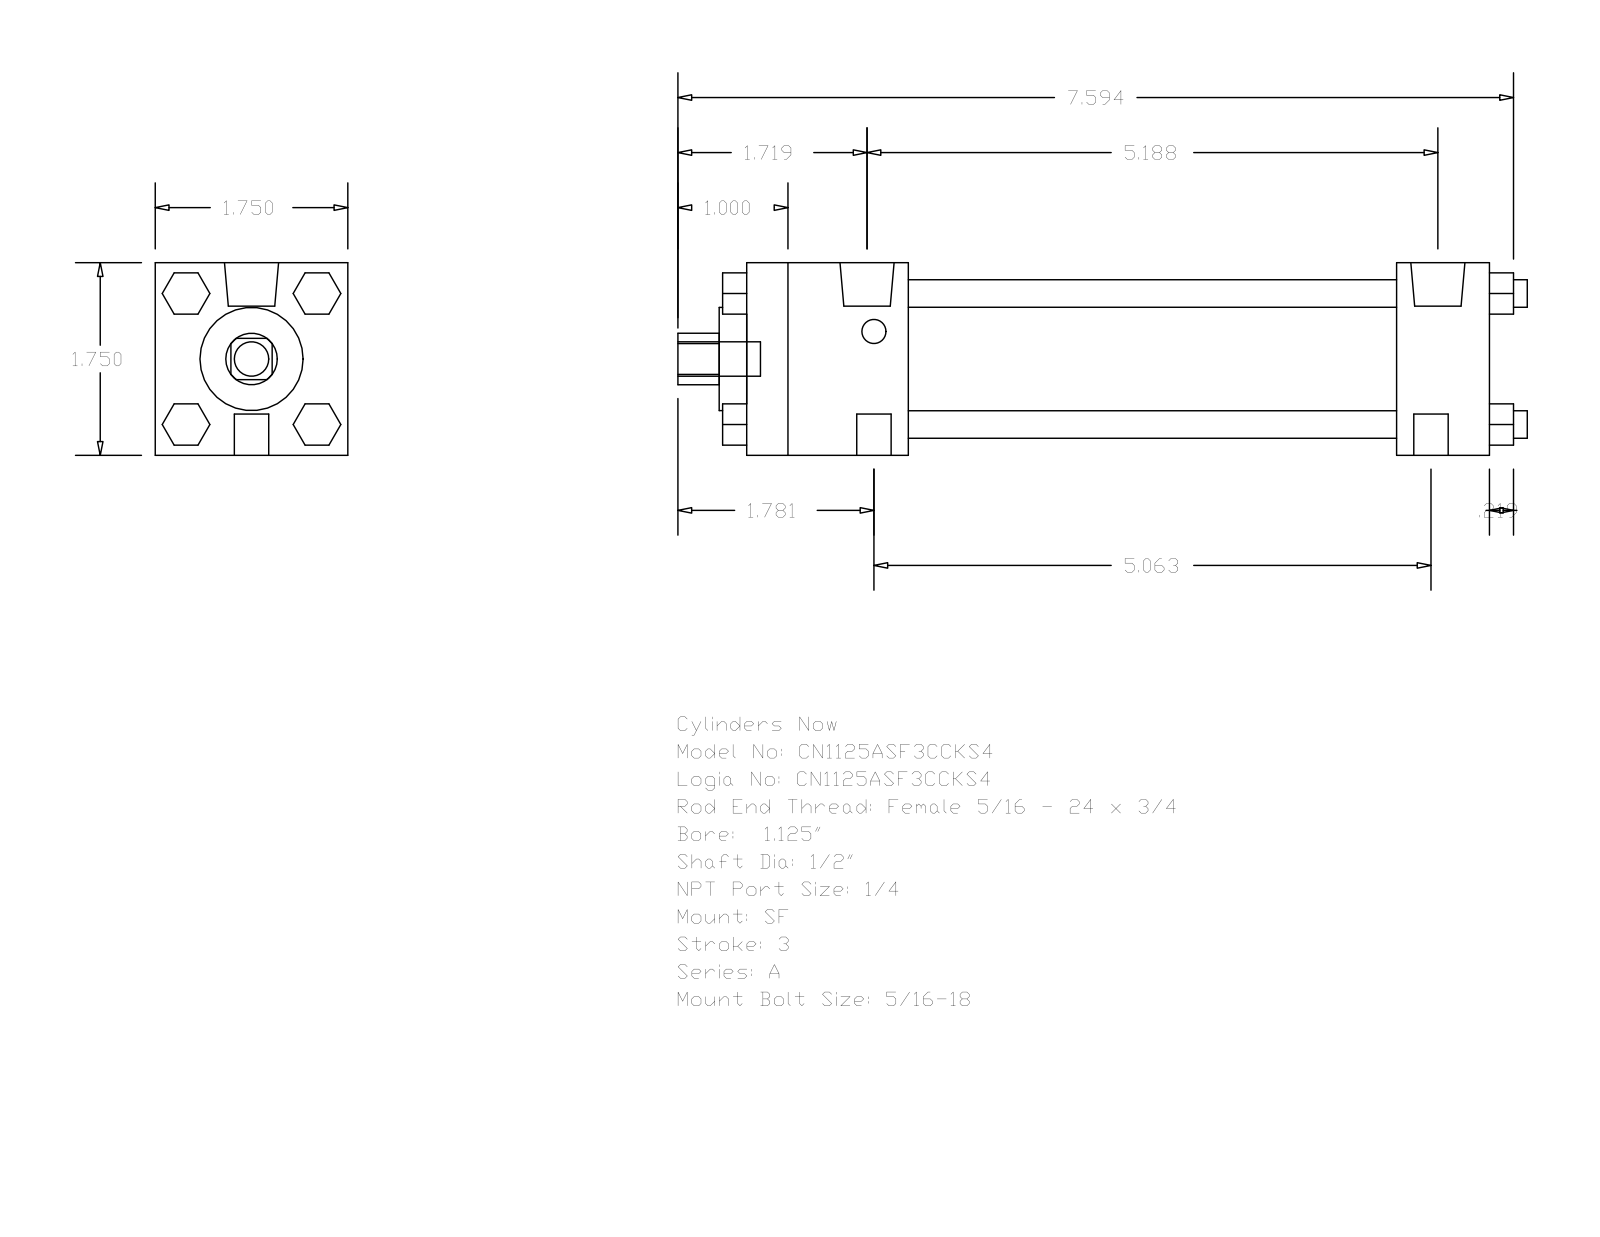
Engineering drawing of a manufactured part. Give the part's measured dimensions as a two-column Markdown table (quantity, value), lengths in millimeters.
| quantity | value |
| --- | --- |
| part name | A_SF__0112_0.5 |
| STEP written by | GSSL Pune (CONFIG_CONTROL_DESIGN) |
| units | millimeters |
| bodies | 0 solids, 120 faces (92 planar, 28 cylindrical, 0 other) |
| overall size | 196.06 × 44.45 × 44.45 |
| round holes (diameter × count) | 12.7 × 1, 23.81 × 1, 31.88 × 1 |
| round bosses / shafts (diameter × count) | 6.35 × 4, 7.94 × 3, 12.49 × 2, 5.56 × 2 |
| partial cylindrical surfaces (radius × count) | 5.94 × 1 |
| main face-to-face distances | 44.46, 171.44, 150.01, 21.43, 37.3, 112.71, 134.14, 9.53, 5.59, 9.52 |
